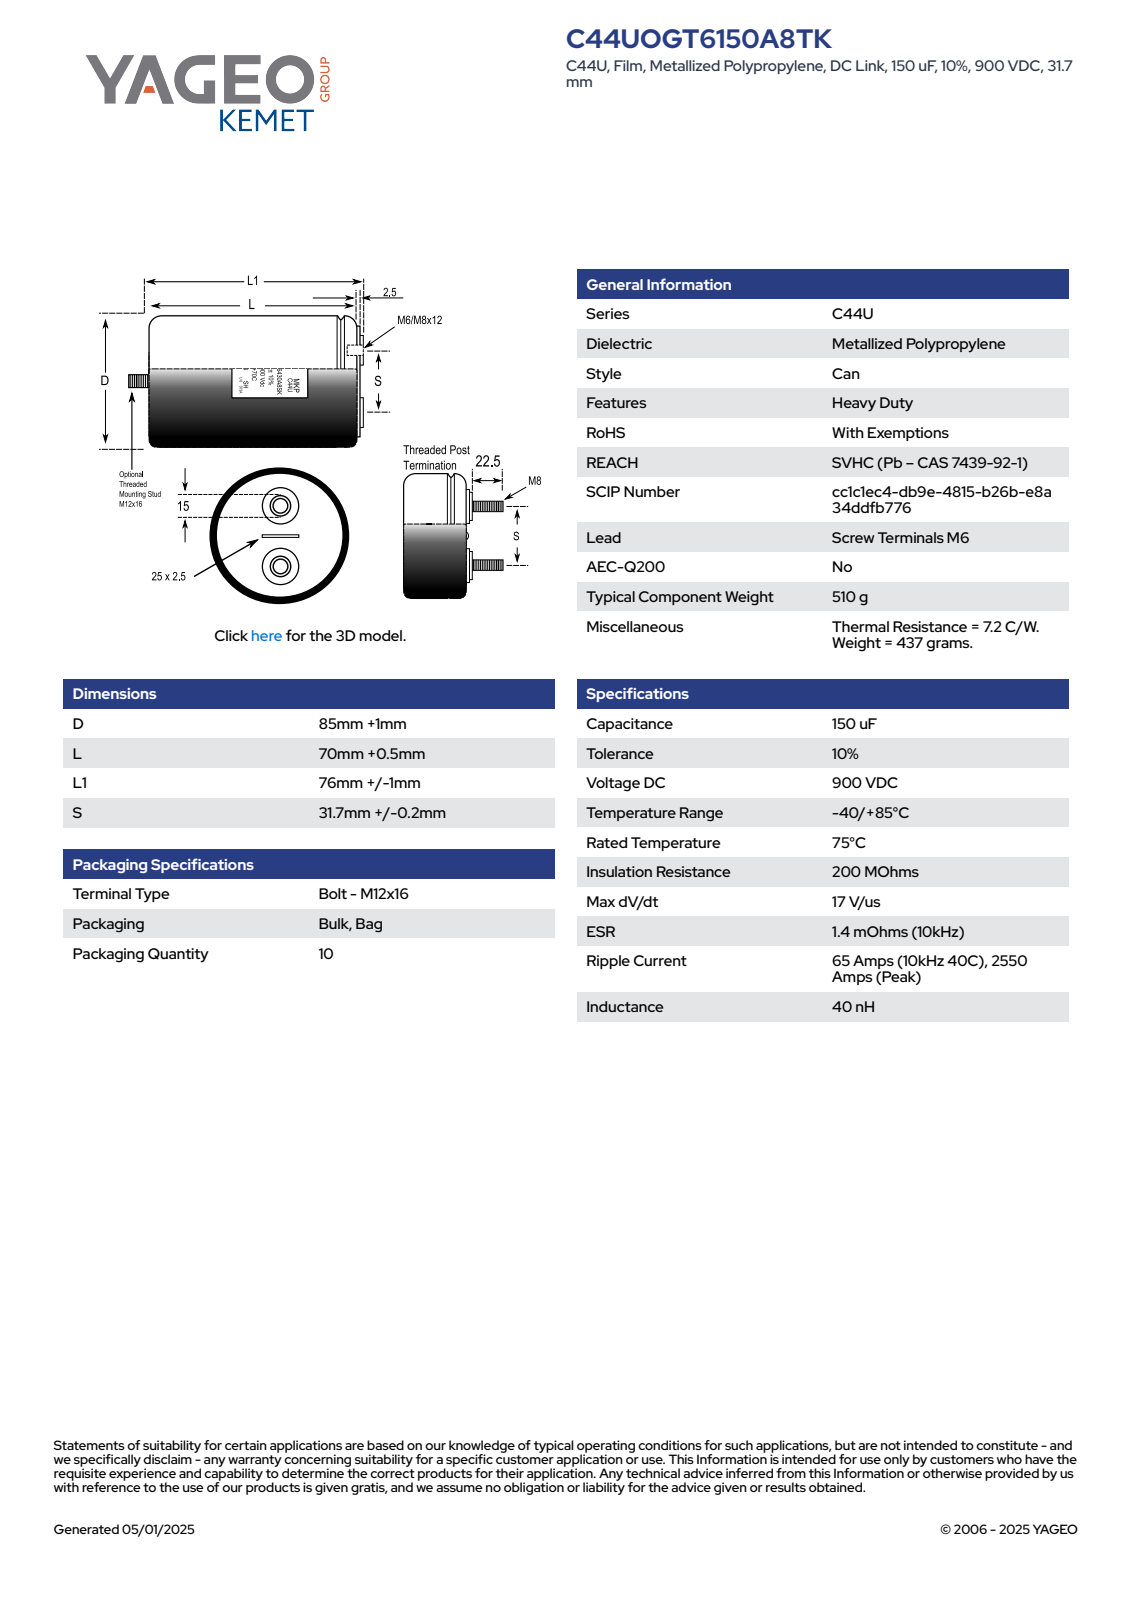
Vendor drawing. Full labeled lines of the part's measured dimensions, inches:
Part name (STEP PRODUCT): CFP_C44U_T_85X70_D86L72S31.9
STEP written by: SolidWorks 2014 (AUTOMOTIVE_DESIGN)
Units: inches
Bodies: 1 solid, 104 faces (36 planar, 29 cylindrical, 39 other)
Overall size (bounding box): 3.563 × 3.386 × 3.386
Volume: 25.18 in³ · Surface area: 47.75 in²
Round holes (diameter × count): ⌀0.236 ×2
Round bosses / shafts (diameter × count): ⌀0.709 ×2, ⌀0.591 ×2, ⌀3.386 ×1, ⌀2.756 ×1, ⌀0.472 ×1
Partial cylindrical surfaces — rounded edges, fillets, slot ends (radius × count): R1.693 ×1
Main face-to-face distances: 2.835, 0.098, 0.049, 2.933, 2.884, 0.63, 3.465, 3.514, 3.563, 3.543
Hole centre spacings: 1.256
